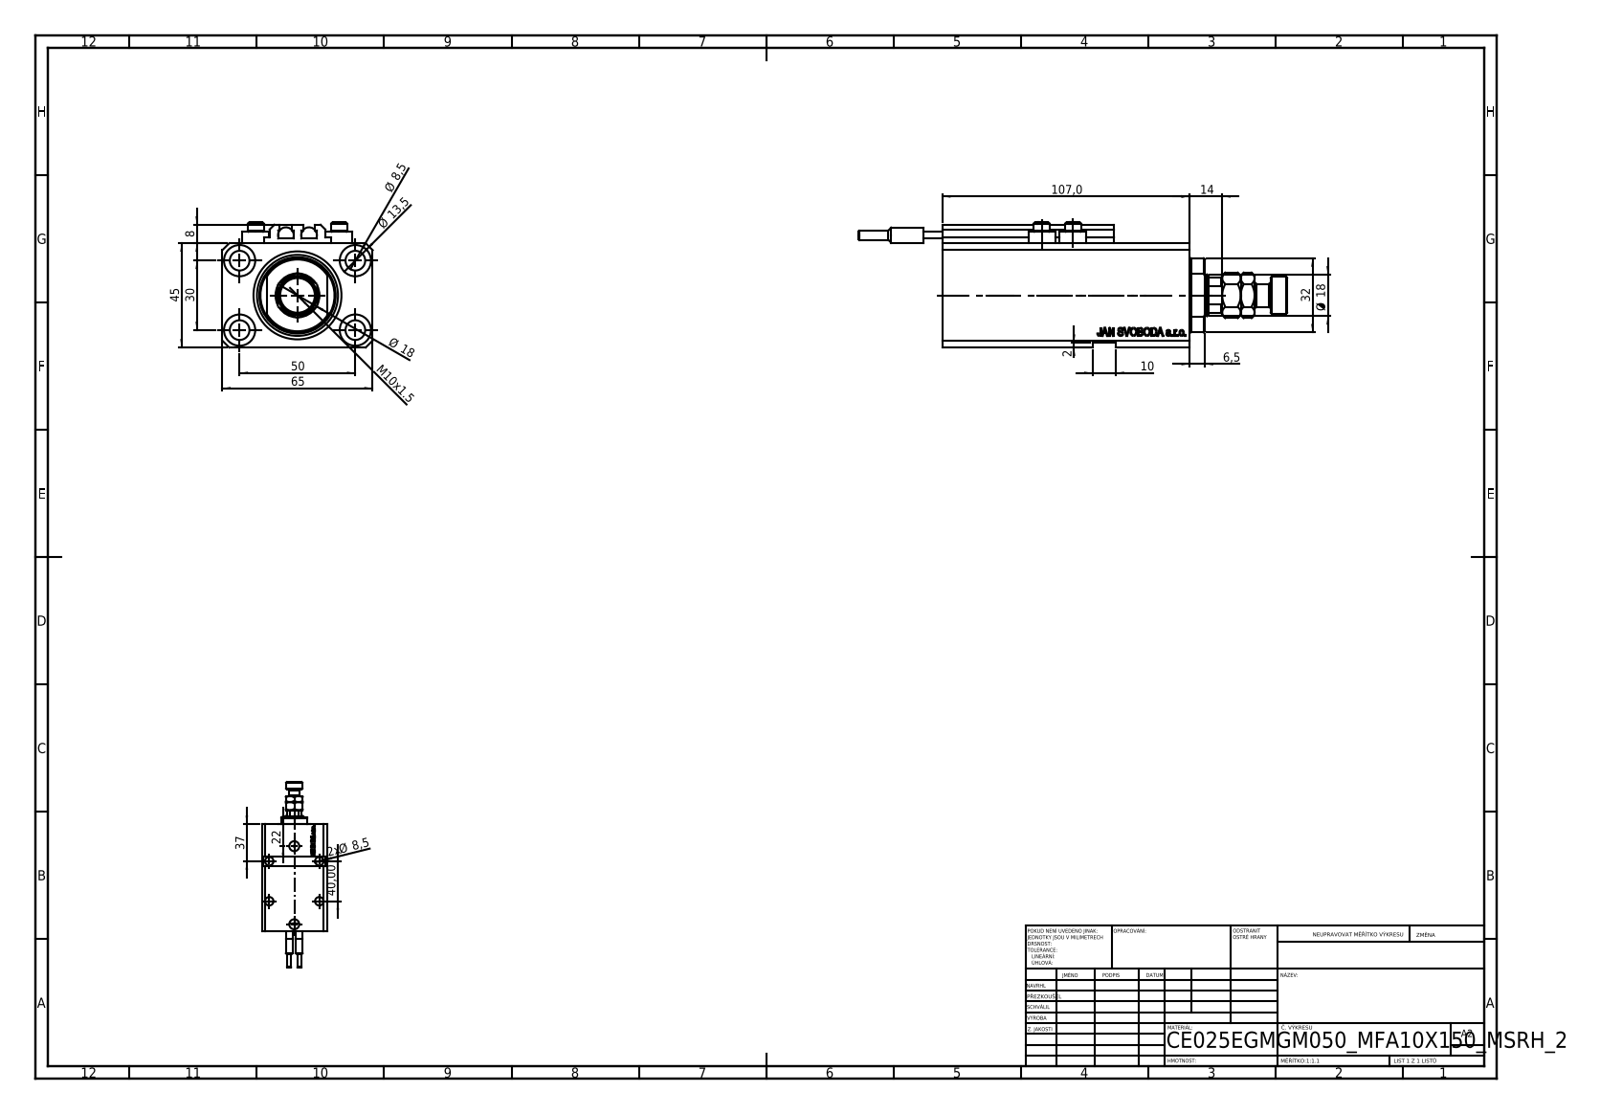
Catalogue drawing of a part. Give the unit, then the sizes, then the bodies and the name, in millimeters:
Units: millimetres
Overall size (bounding box): 185 × 65 × 54
Round holes (diameter × count): ⌀8.5 ×9, ⌀1.25 ×4, ⌀4 ×4, ⌀13.5 ×4, ⌀10 ×2, ⌀13.16 ×2, ⌀20 ×2, ⌀18 ×1, ⌀25 ×1, ⌀38 ×1
Round bosses / shafts (diameter × count): ⌀11.6 ×4, ⌀7 ×4, ⌀6.8 ×2, ⌀6.5 ×2, ⌀4 ×2, ⌀16 ×1, ⌀10 ×1
Partial cylindrical surfaces — rounded edges, fillets, slot ends (radius × count): R0.2 ×10, R8.5 ×1, R16 ×1
Main face-to-face distances: 45, 65, 14, 2, 47, 93, 3, 107, 6.9, 10
Hole centre spacings: 29.15, 50, 13.6, 14.76, 15.12, 27.51, 27.89, 30
Volume: 282 398 mm³ · Surface area: 81 691 mm²
Bodies: 11 solids, 1191 faces (559 planar, 162 cylindrical, 470 other)
Part name (STEP PRODUCT): ALLEN BOLT V250CE; V250CE_C_VCP; SWITCH_V250CE; MFA (+2 more)
STEP written by: SolidWorks 2019 (CONFIG_CONTROL_DESIGN)
